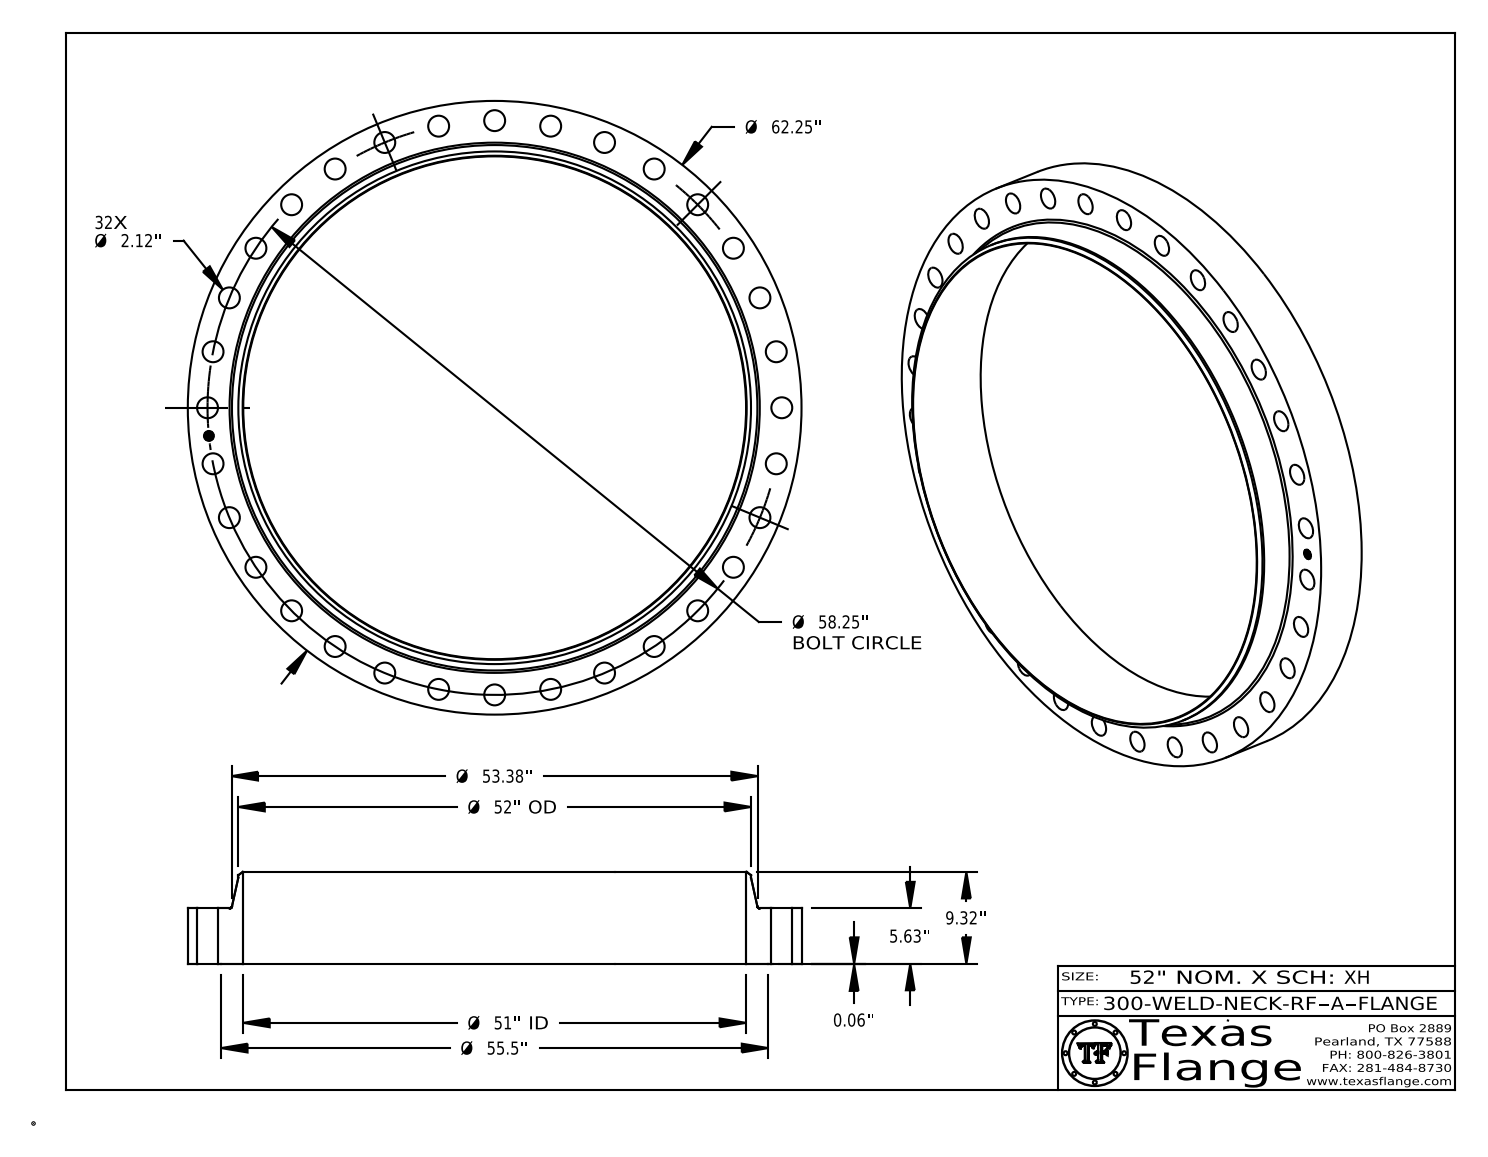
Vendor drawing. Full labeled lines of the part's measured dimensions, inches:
Part name (STEP PRODUCT): 300-WELD-NECK-RF, Series A
STEP written by: CATIA V5 STEP AP214 (AUTOMOTIVE_DESIGN)
Units: inches
Bodies: 1 solid, 467 faces (369 planar, 92 cylindrical, 6 other)
Overall size (bounding box): 62.25 × 62.25 × 9.383
Volume: 5 487 in³ · Surface area: 6 052 in²
Round holes (diameter × count): ⌀2.12 ×32, ⌀1 ×1, ⌀51 ×1
Round bosses / shafts (diameter × count): ⌀0.061 ×8, ⌀62.25 ×1, ⌀55.5 ×1, ⌀52 ×1, ⌀0.788 ×1
Main face-to-face distances: 5.63, 0.063, 5.693, 9.383, 9.32, 3.69, 0.015, 5.678, 5.615, 3.705
Hole centre spacings: 45.028, 48.433, 57.131, 41.189, 22.291, 5.709, 16.909, 32.362
